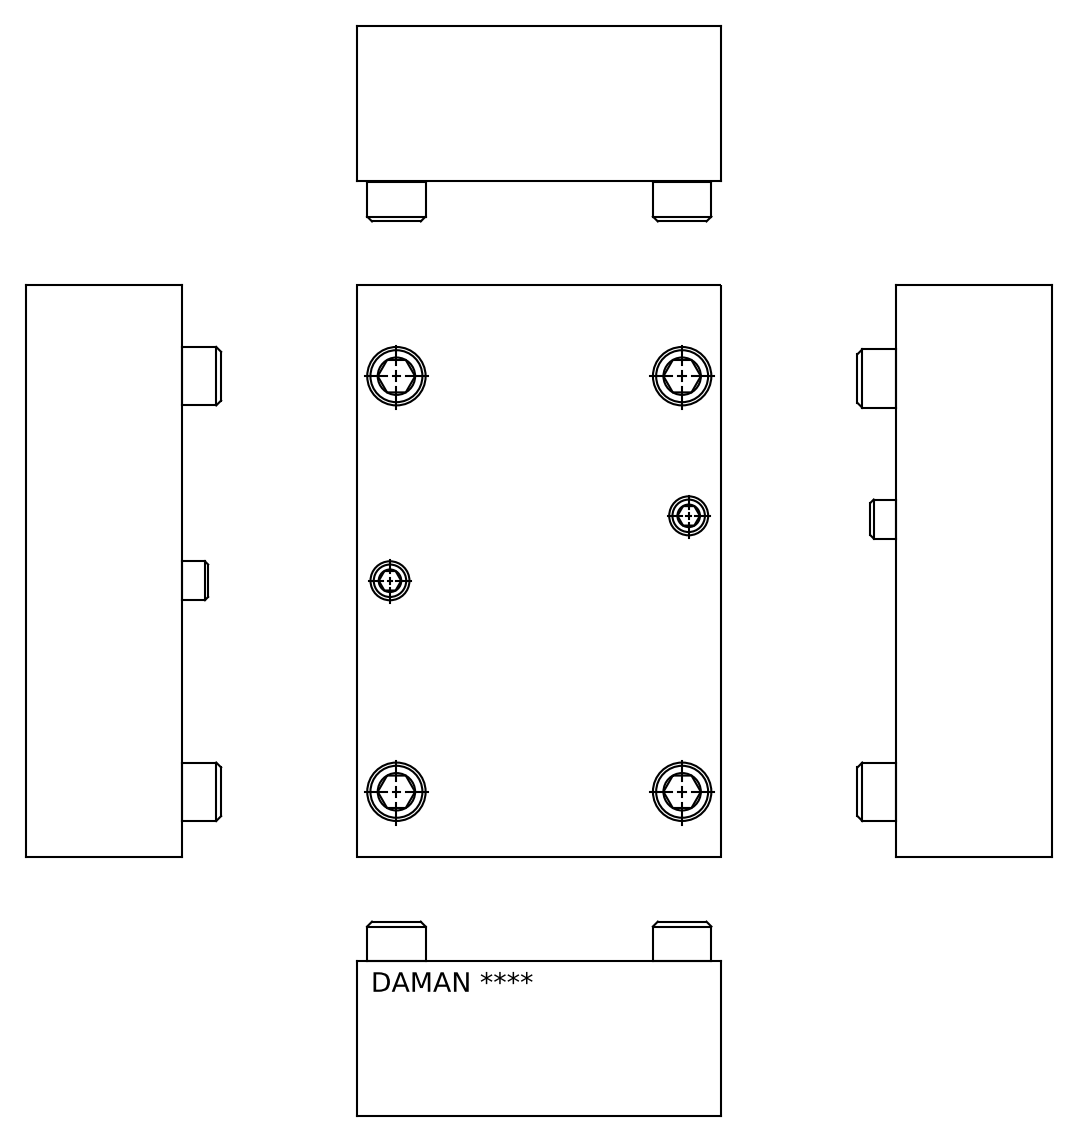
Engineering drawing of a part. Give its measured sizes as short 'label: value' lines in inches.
name: D07CPS
written by: Autodesk Inventor 2020 (AUTOMOTIVE_DESIGN)
unit: in
bodies: 1 solid, 292 faces (204 planar, 16 cylindrical, 72 other)
size: 5 × 3.5 × 1.5
volume: 24.98 in³; area: 71.14 in²
holes: 4× ⌀0.406, 4× ⌀1, 2× ⌀0.125, 2× ⌀0.281, 2× ⌀0.438, 2× ⌀0.688
face distances: 1.5, 3.5, 5, 0.04, 1.46, 4.99, 0.09, 0.045, 0.016, 0.211
hole spacings: 1.741, 0.884, 0.884, 1.25, 2.25, 2.574, 2.75, 4
